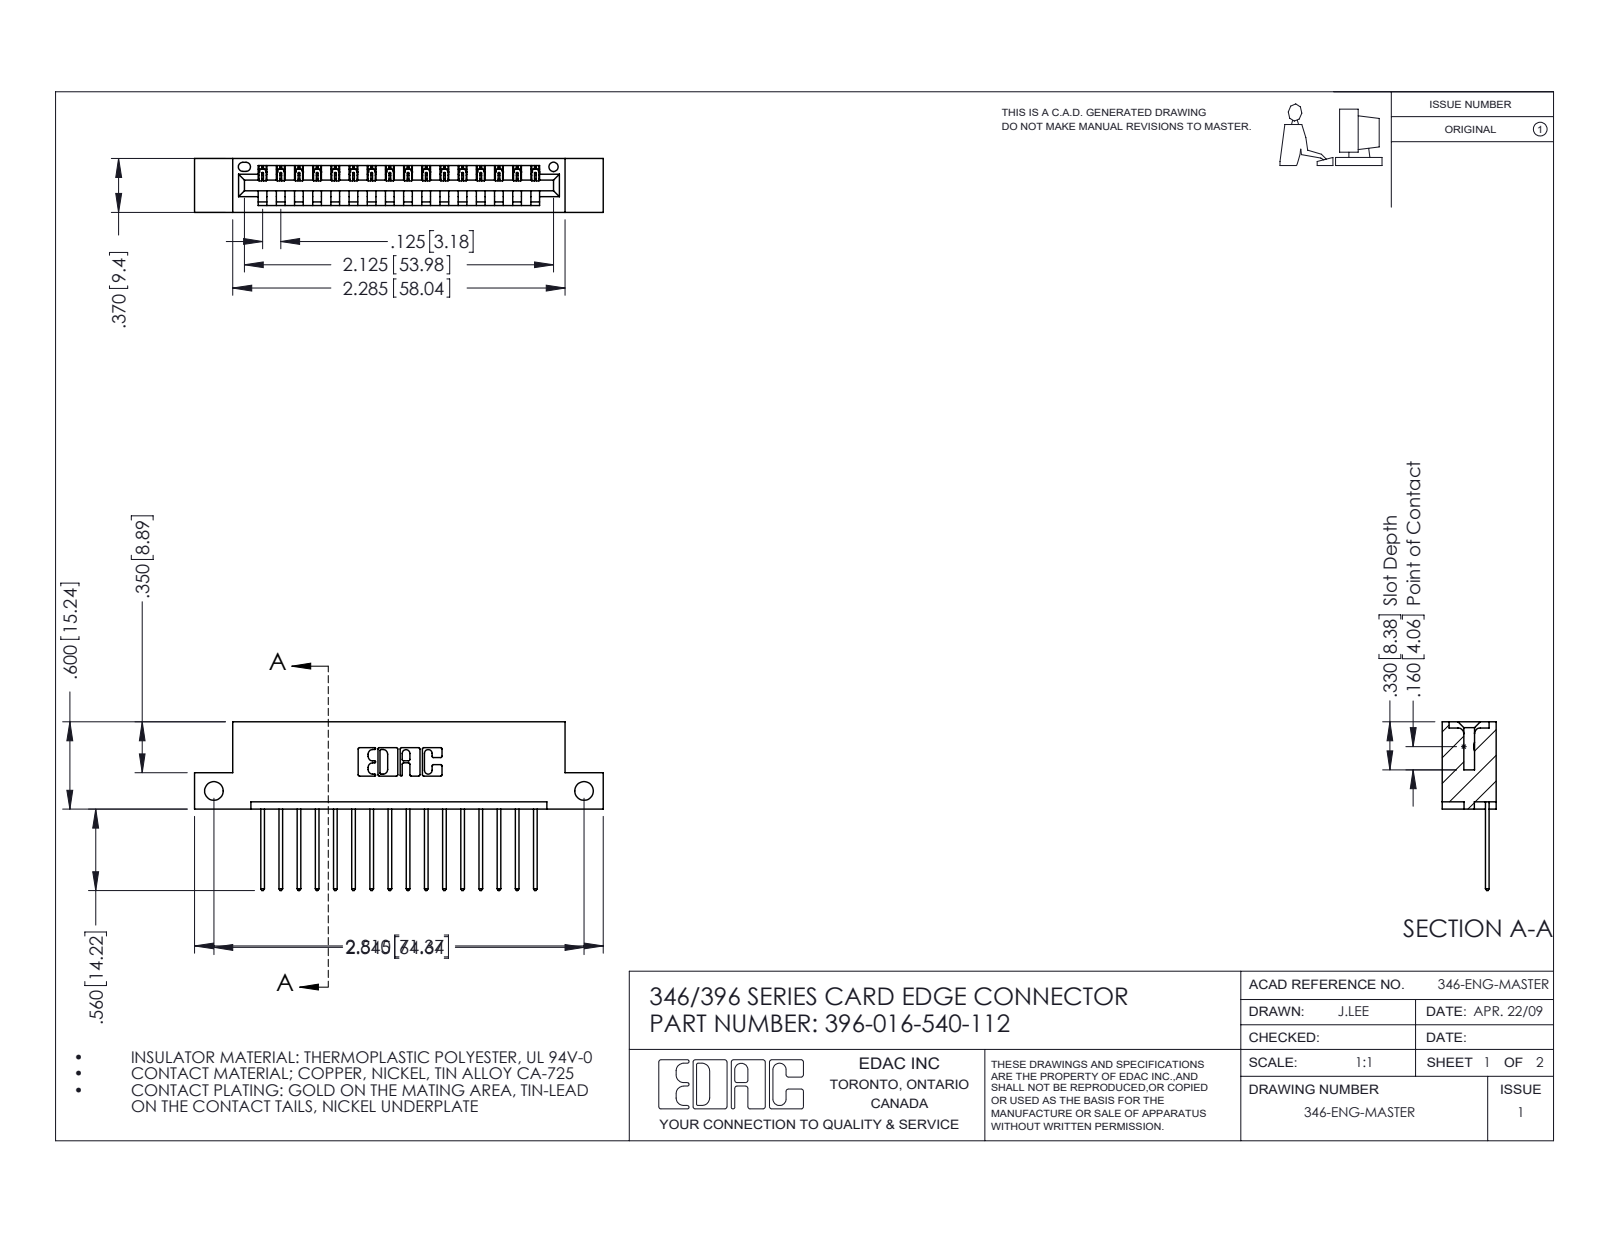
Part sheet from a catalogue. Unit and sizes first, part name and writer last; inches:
Units: inches
Overall size (bounding box): 2.81 × 1.16 × 0.37
Round holes (diameter × count): ⌀0.128 ×2, ⌀0.064 ×1
Partial cylindrical surfaces — rounded edges, fillets, slot ends (radius × count): R0.006 ×32, R0.01 ×32, R0.01 ×22, R0.007 ×6, R0.031 ×6, R0.026 ×3, R0.031 ×2, R0.04 ×2
Main face-to-face distances: 0.048, 0.322, 0.25, 0.37, 0.072, 0.298, 0.025, 0.148, 0.222, 0.1
Hole centre spacings: 2.545
Volume: 0.402 in³ · Surface area: 12.35 in²
Bodies: 17 solids, 1050 faces (716 planar, 334 cylindrical, 0 other)
Part name (STEP PRODUCT): 345-292-001_345-293-140; 346 Part_Flush Mounting Lugs - Side Mount; 396-016-540-112
STEP written by: SolidWorks 2016 (CONFIG_CONTROL_DESIGN)
